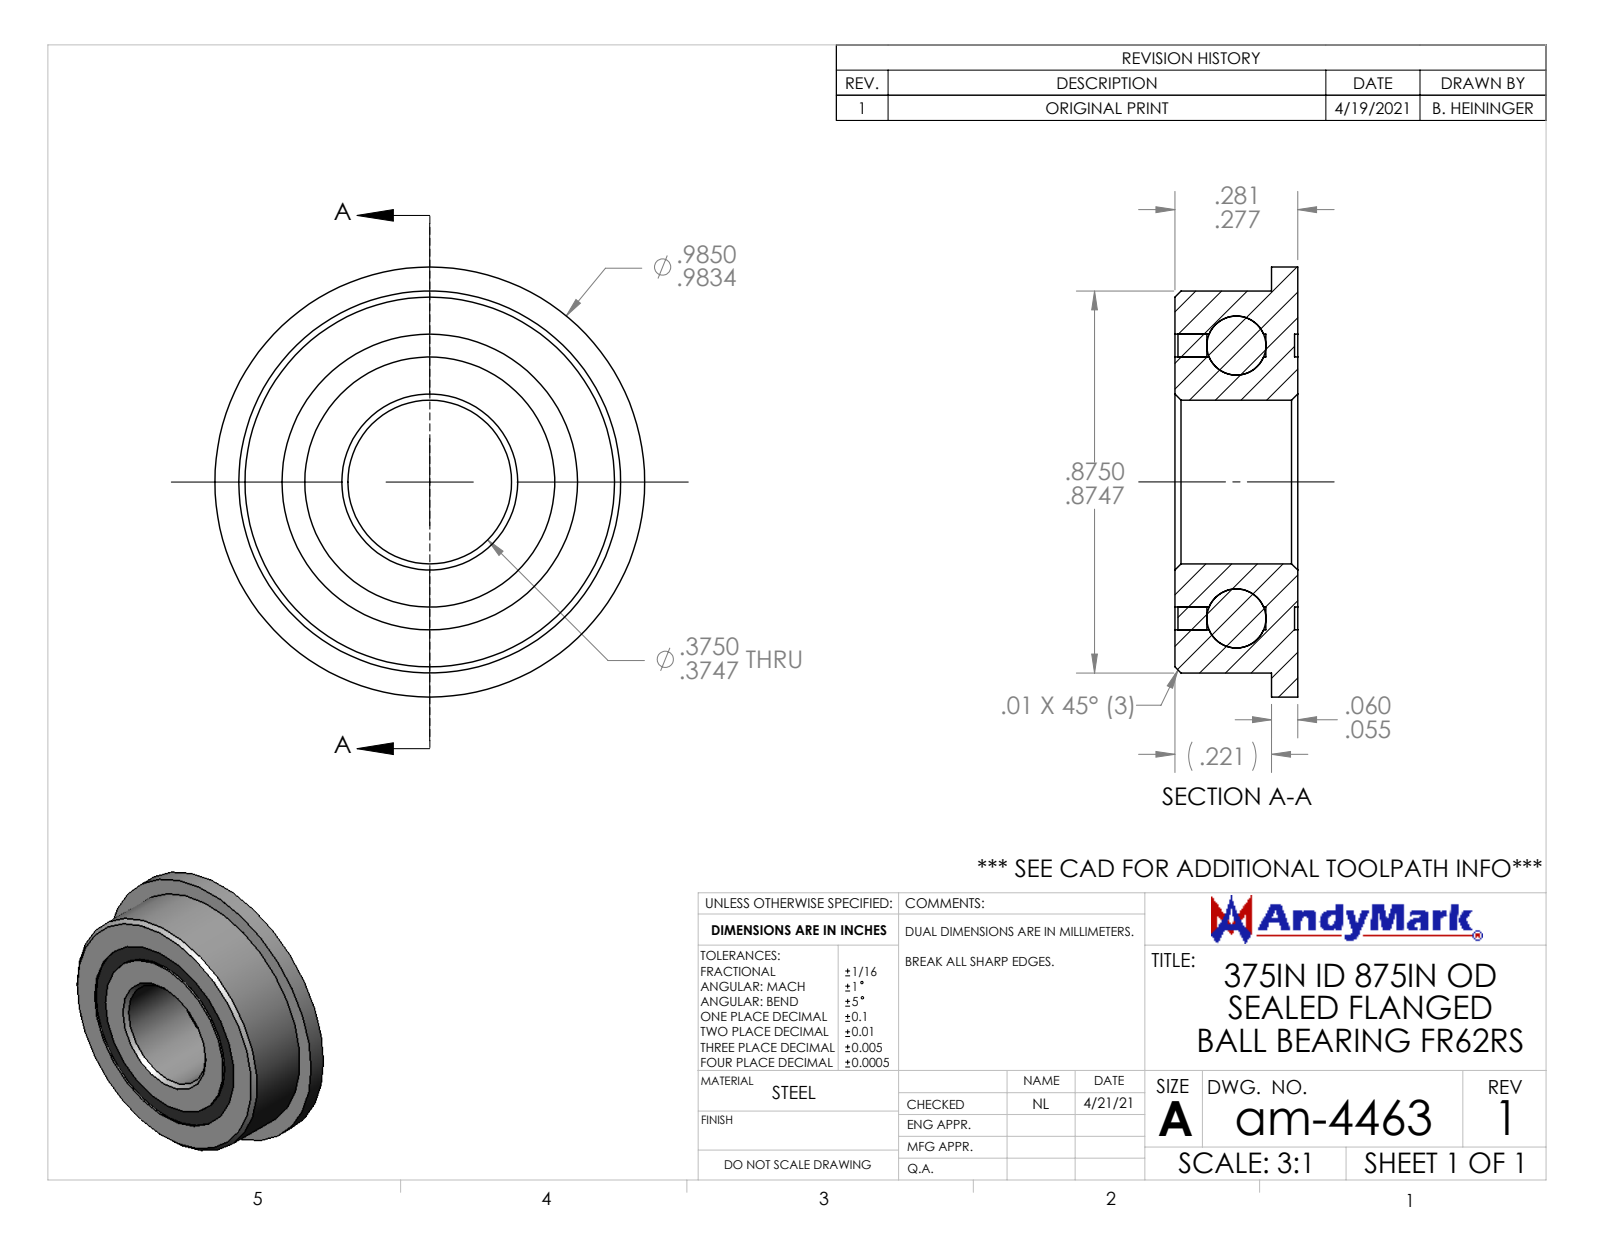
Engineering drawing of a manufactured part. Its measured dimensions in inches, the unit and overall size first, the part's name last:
Units: inches
Overall size (bounding box): 0.985 × 0.985 × 0.281
Round holes (diameter × count): ⌀0.375 ×1, ⌀0.677 ×1
Round bosses / shafts (diameter × count): ⌀0.985 ×1, ⌀0.875 ×1, ⌀0.573 ×1
Main face-to-face distances: 0.281, 0.274, 0.073, 0.208, 0.066, 0.201, 0.221, 0.06, 0.214, 0.148
Volume: 0.13 in³ · Surface area: 4.407 in²
Bodies: 12 solids, 63 faces (9 planar, 22 cylindrical, 32 other)
Part name (STEP PRODUCT): am-4463 3-8 in ID 7-8 in OD Sealed Flanged Bearing FR62RS
STEP written by: SolidWorks 2019 (AUTOMOTIVE_DESIGN)
